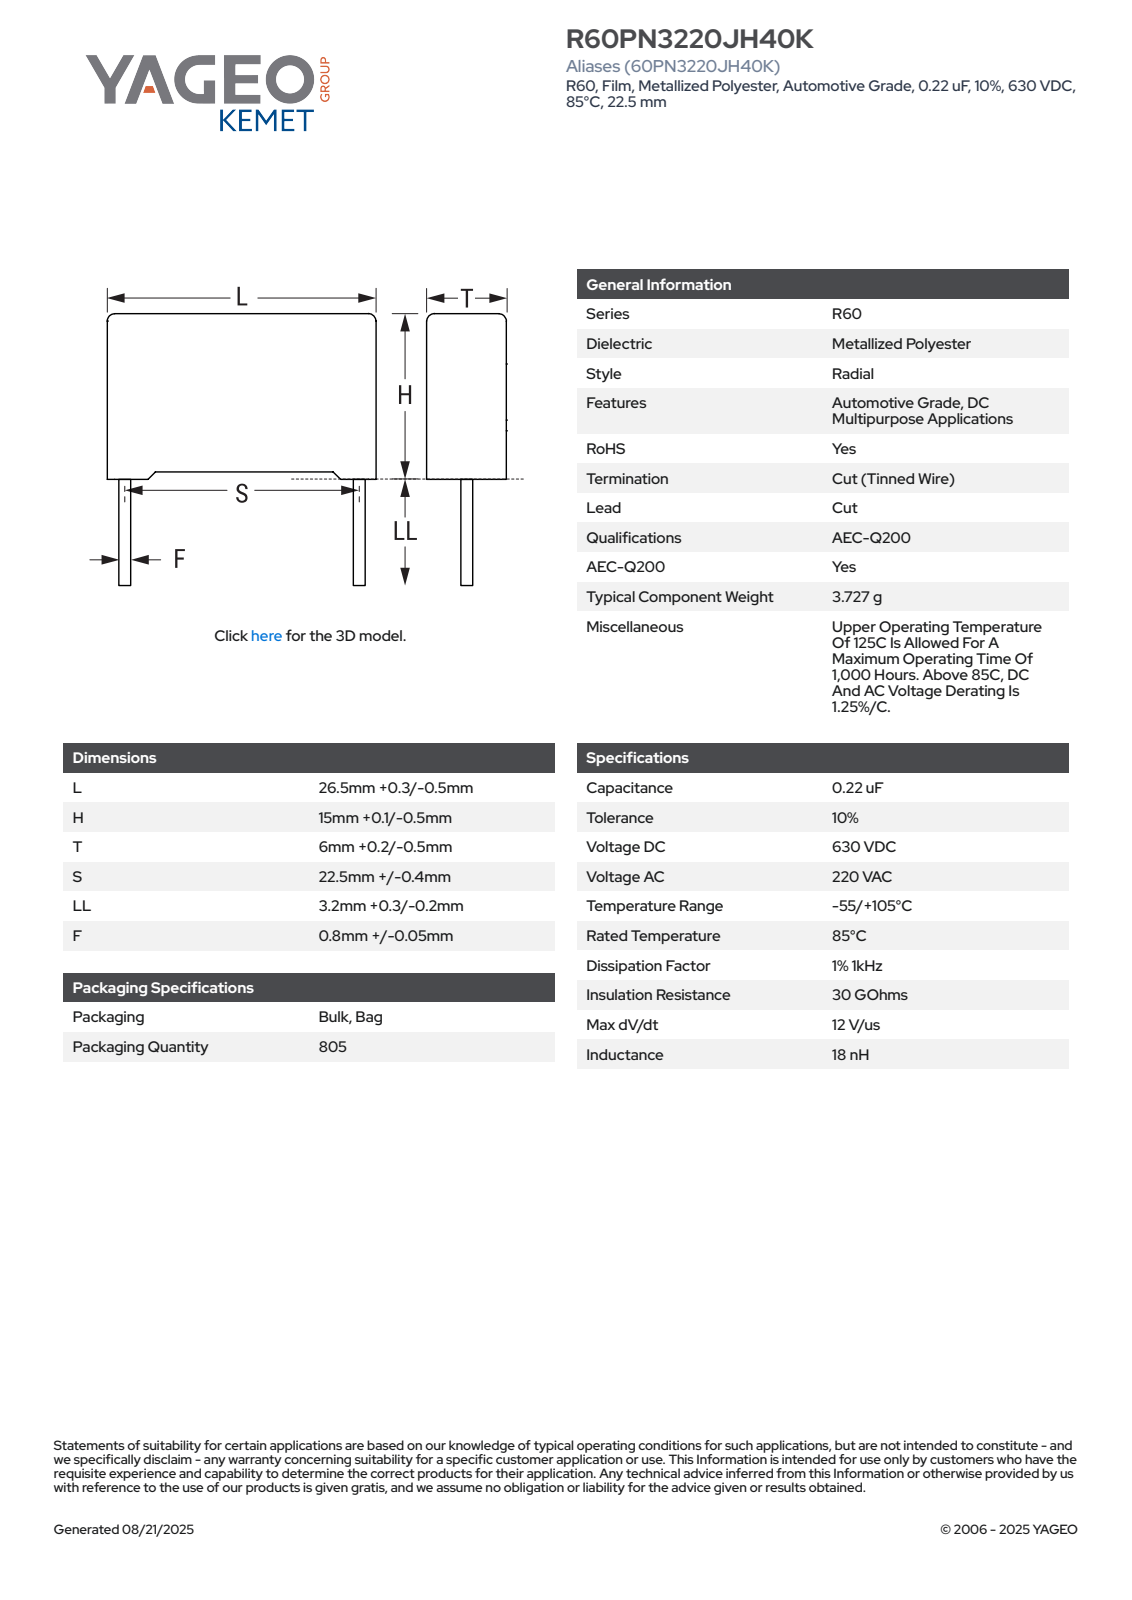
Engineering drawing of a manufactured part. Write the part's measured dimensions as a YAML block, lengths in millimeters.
part_name: "CFR_RB2_26.5X15X6_L26.8H15.1T6.2S22.5LL3.5F0.85"
step_written_by: "SolidWorks 2021 (AUTOMOTIVE_DESIGN)"
units: millimeters
bodies: {solids: 4, faces: 85, planar: 77, cylindrical: 8, other: 0}
overall_size: [26.8, 18.6, 6.21]
volume: 2410
surface_area: 1397
round_bosses_or_shafts:
  - {diameter: 0.85, count: 2}
partial_cylinders:
  - {radius: 0.5, count: 4}
face_to_face_distances: [6.2, 14.35, 26.8, 14.58, 0.89, 0.52, 0.75, 15.1, 5.31, 4.42]
